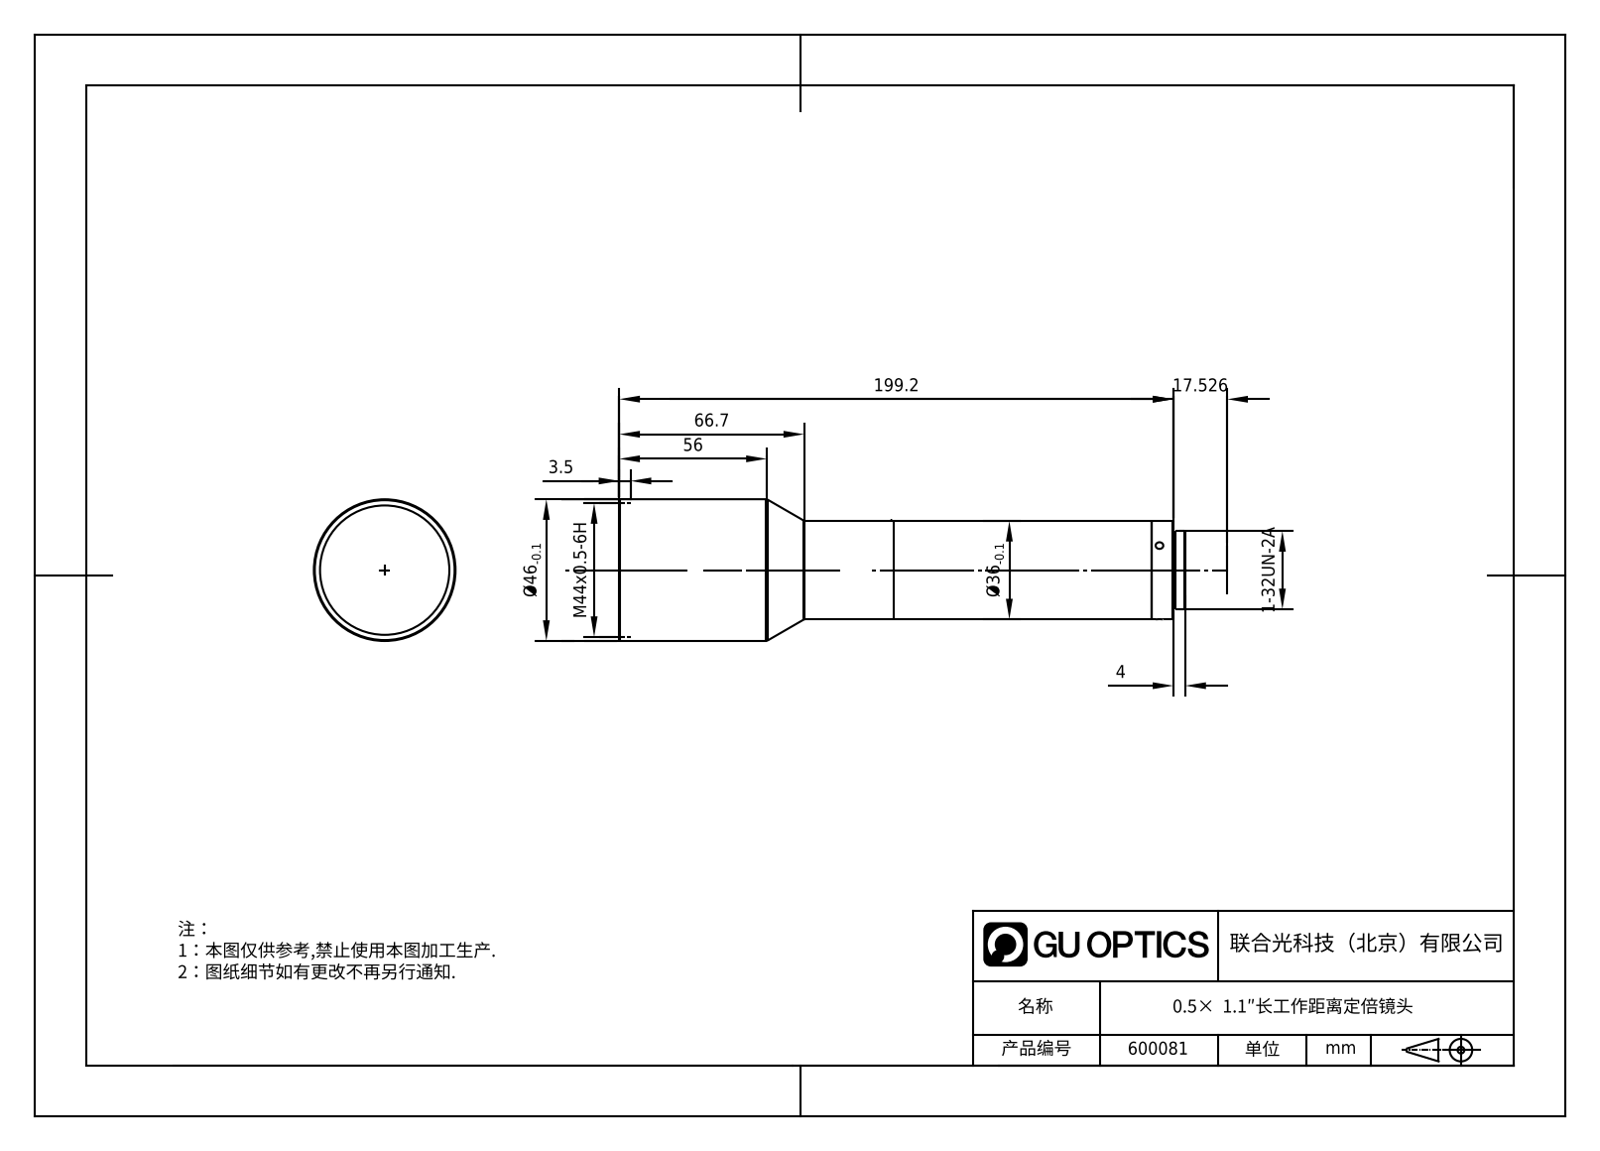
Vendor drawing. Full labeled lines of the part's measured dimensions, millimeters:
Part name (STEP PRODUCT): 600081
STEP written by: SolidWorks 2020 (CONFIG_CONTROL_DESIGN)
Units: millimetres
Bodies: 2 solids, 28 faces (7 planar, 12 cylindrical, 9 other)
Overall size (bounding box): 203.15 × 46 × 46
Volume: 238 081 mm³ · Surface area: 31 948 mm²
Round holes (diameter × count): ⌀2.5 ×3, ⌀42 ×1
Round bosses / shafts (diameter × count): ⌀46 ×1, ⌀36 ×1, ⌀25.4 ×1, ⌀24.6 ×1
Partial cylindrical surfaces — rounded edges, fillets, slot ends (radius × count): R17.13 ×1
Main face-to-face distances: 190.15, 4, 194.15, 203.15, 199.15, 9, 3.2, 0.8, 190.95, 199.95
